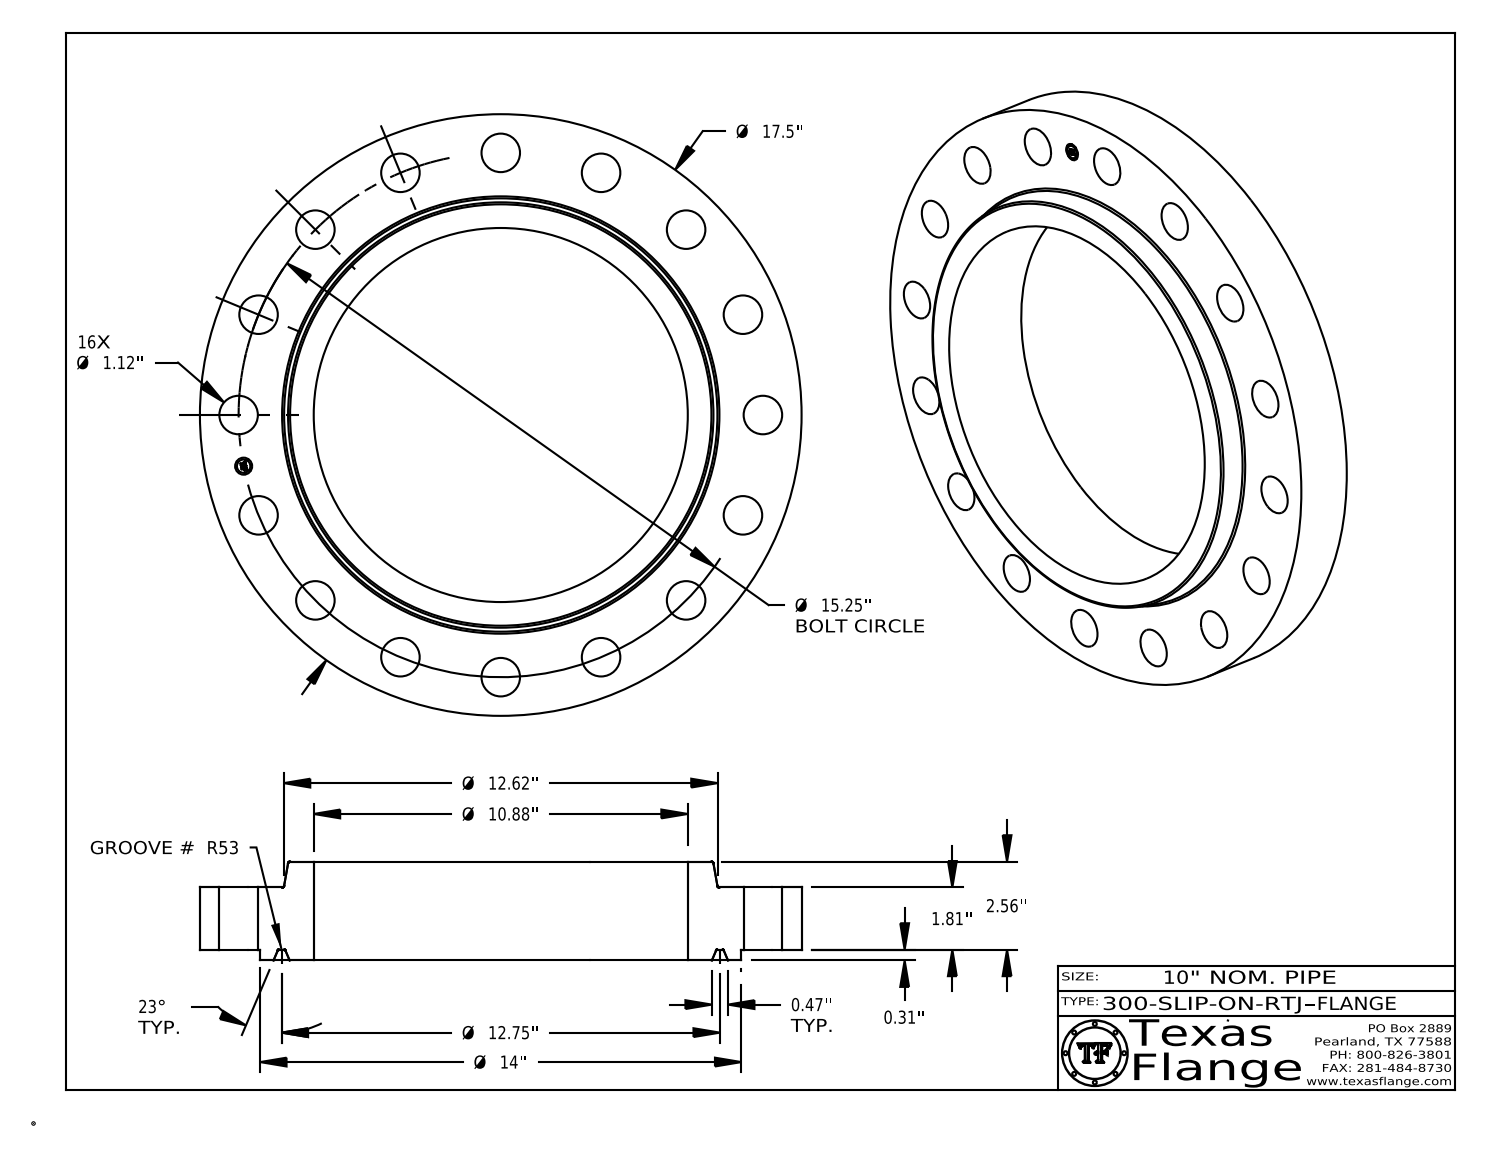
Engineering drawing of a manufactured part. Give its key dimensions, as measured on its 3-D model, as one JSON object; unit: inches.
{"part_name": "300-SLIP-ON-RTJ", "step_written_by": "CATIA V5 STEP AP214 (AUTOMOTIVE_DESIGN)", "units": "inches", "bodies": {"solids": 1, "faces": 443, "planar": 371, "cylindrical": 58, "other": 14}, "overall_size": [17.5, 17.5, 2.873], "volume_in3": 275.5, "surface_area_in2": 616.6, "round_holes": [[1.12, 16], [0.495, 1], [10.88, 1]], "round_bosses_or_shafts": [[0.03, 8], [17.5, 1], [14, 1], [0.39, 1]], "face_to_face_distances": [1.81, 0.313, 2.122, 2.872, 2.56, 0.75, 0.015, 2.107, 1.795, 0.765], "hole_center_spacings": [8.472, 10.783, 14.957, 14.089, 7.625, 2.975, 2.975, 5.836]}
